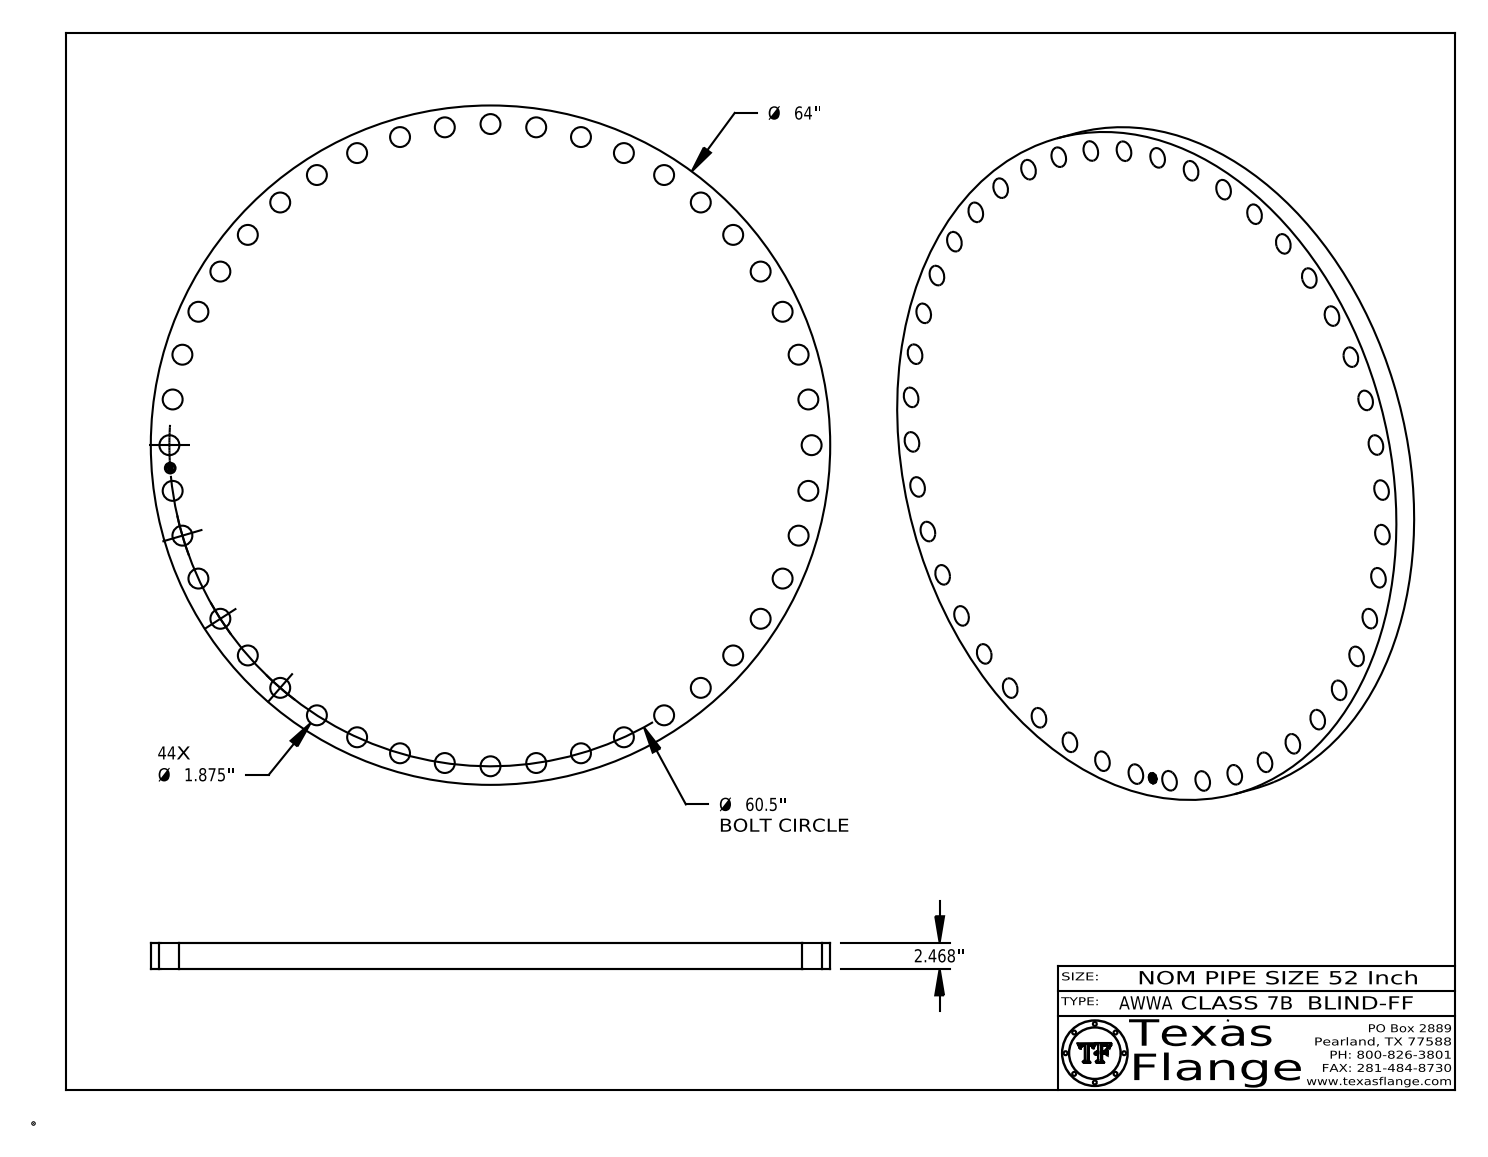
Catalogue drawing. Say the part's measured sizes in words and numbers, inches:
The part is named "AWWA Class 7B-BLIND-FF". Its 3-D file was written by "CATIA V5 STEP AP214 (AUTOMOTIVE_DESIGN)". It is 1 solid with 477 faces: 367 planar, 110 cylindrical and 0 other. Overall it measures 64 by 64 by 2.468 inches. Its volume is 7 640 cubic inches and its surface area 7 327 square inches. Round holes: 44 of diameter 1.875, 1 of diameter 1. Round bosses or shafts: 8 of diameter 0.061, 1 of diameter 64, 1 of diameter 0.788. The main face-to-face distances are 2.468, 0.015, 2.453, 0.298, 0.292, 0.019, 0.054, 0.193, 0.248, 0.044. The hole center spacings are 4.316, 8.61, 21.143, 25.133, 17.045, 42.78, 48.433, 59.884.
